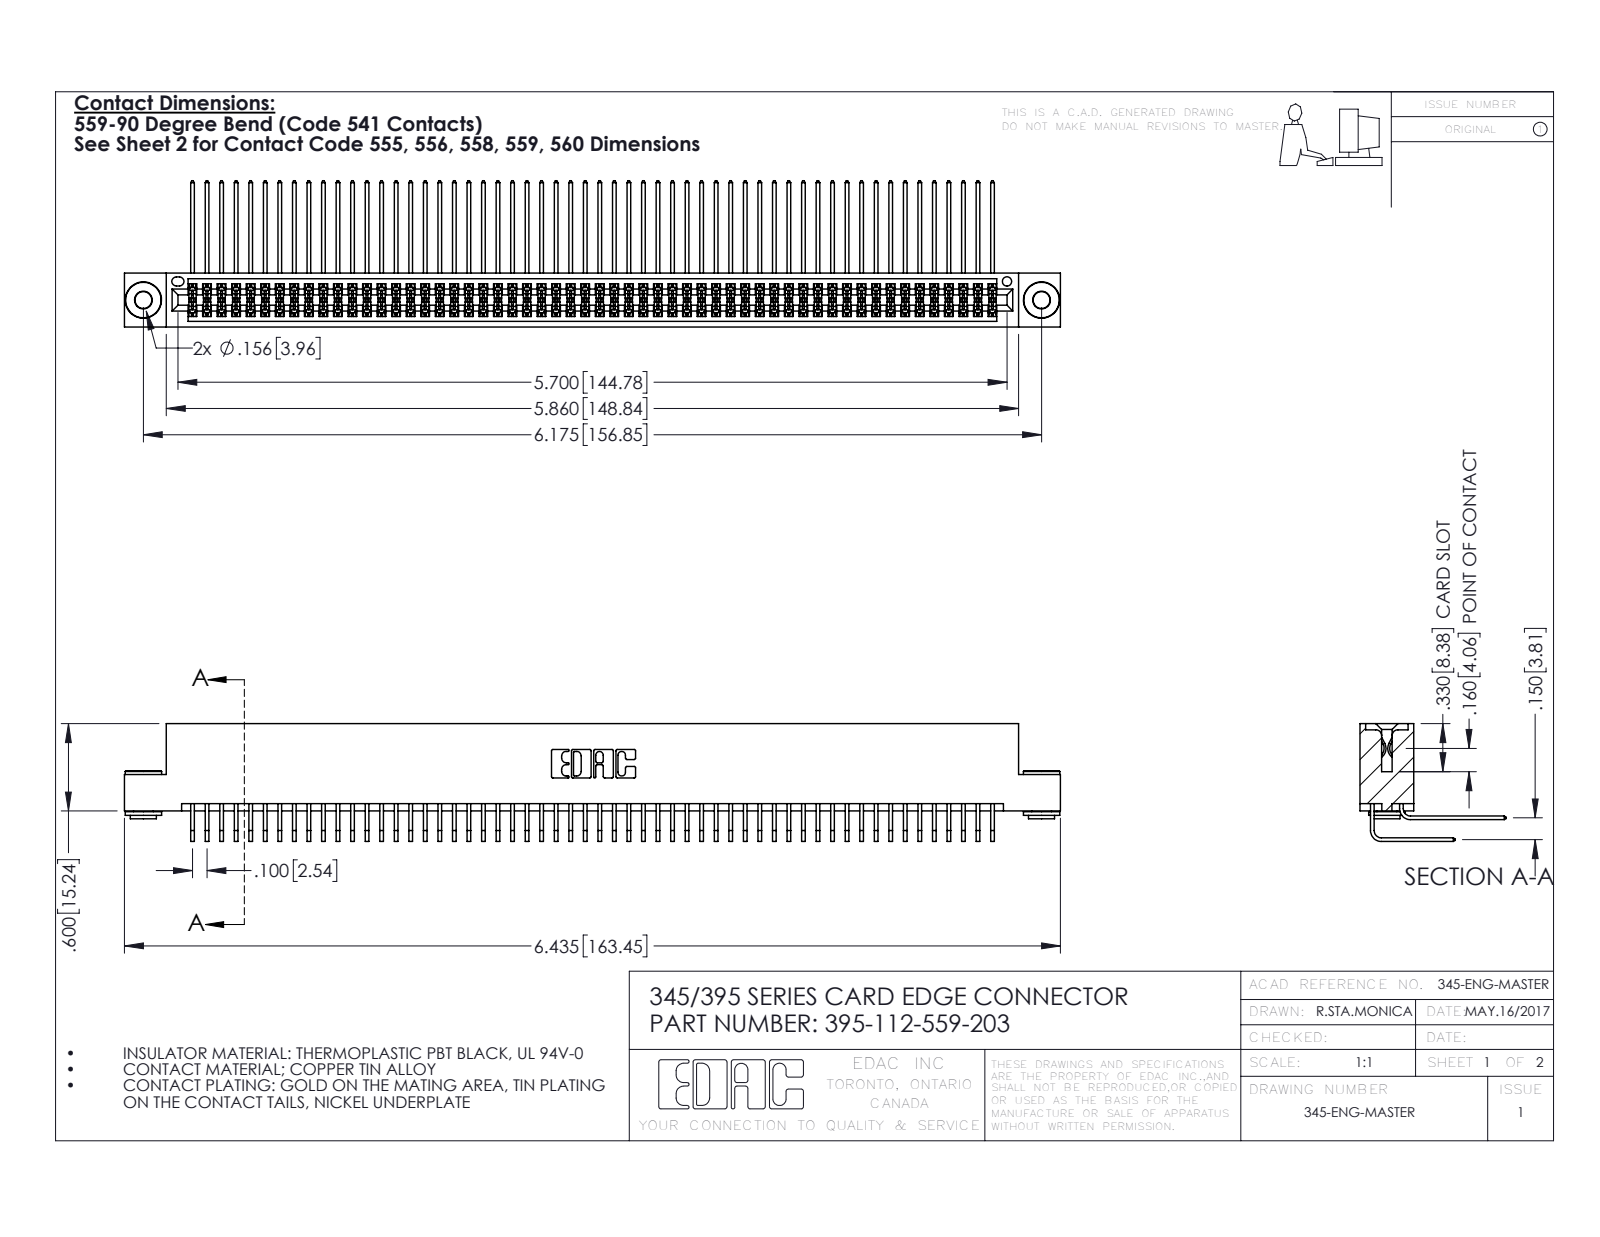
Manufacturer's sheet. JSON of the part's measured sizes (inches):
{"part_name": "395-112-559-203; 345 Part_Flush Mounting Lugs - 0.156 Dia-TH; 345-292-001_559 Tail - 2; 345-292-001_558 559 Tail - 1 (+1 more)", "step_written_by": "SolidWorks 2016 (CONFIG_CONTROL_DESIGN)", "units": "inches", "bodies": {"solids": 115, "faces": 5988, "planar": 4010, "cylindrical": 1970, "other": 8}, "overall_size": [6.435, 1.005, 0.809], "volume_in3": 1.017, "surface_area_in2": 43.65, "round_holes": [[0.116, 2], [0.156, 2], [0.064, 1]], "round_bosses_or_shafts": [[0.25, 2], [0.18, 2], [0.136, 2]], "partial_cylinders_radius": [[0.006, 169], [0.01, 22], [0.007, 6], [0.031, 6], [0.026, 3], [0.014, 2], [0.019, 2], [0.022, 2]], "face_to_face_distances": [0.072, 0.298, 0.2, 0.37, 0.025, 0.098, 0.272, 0.225, 0.175, 0.15], "hole_center_spacings": [0.27, 5.939, 6.175]}
